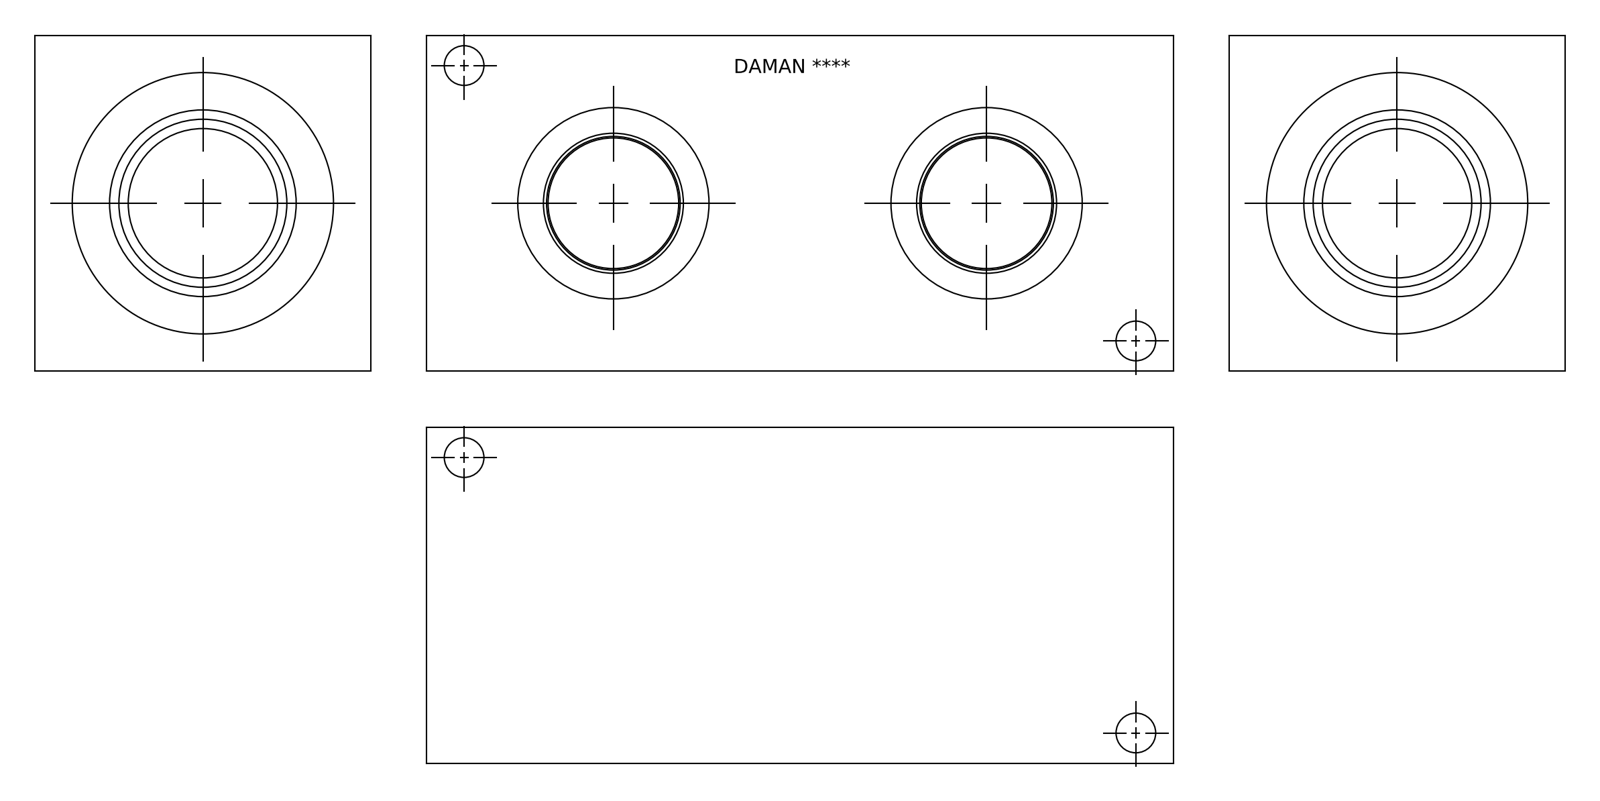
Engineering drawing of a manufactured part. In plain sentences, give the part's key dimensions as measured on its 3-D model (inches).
The part is named "Part_+H0000224S_3D". Its 3-D file was written by "Autodesk Inventor 2020 (AUTOMOTIVE_DESIGN)". It is 1 solid with 362 faces: 224 planar, 28 cylindrical and 110 other. Overall it measures 10 by 4.5 by 4.5 inches. Its volume is 175.4 cubic inches and its surface area 285.7 square inches. Round holes: 4 of diameter 0.531, 2 of diameter 1.688, 2 of diameter 1.794, 2 of diameter 1.875, 2 of diameter 1.892, 2 of diameter 2.564, 1 of diameter 2, 1 of diameter 2.419, 1 of diameter 2.5, 1 of diameter 2.518, 1 of diameter 3.47. The main face-to-face distances are 4.5, 0.031, 10, 9.969, 4.469, 9.938, 0.781, 0.75, 9.219, 9.188. The hole center spacings are 2.72, 7.239, 9.726, 5.
